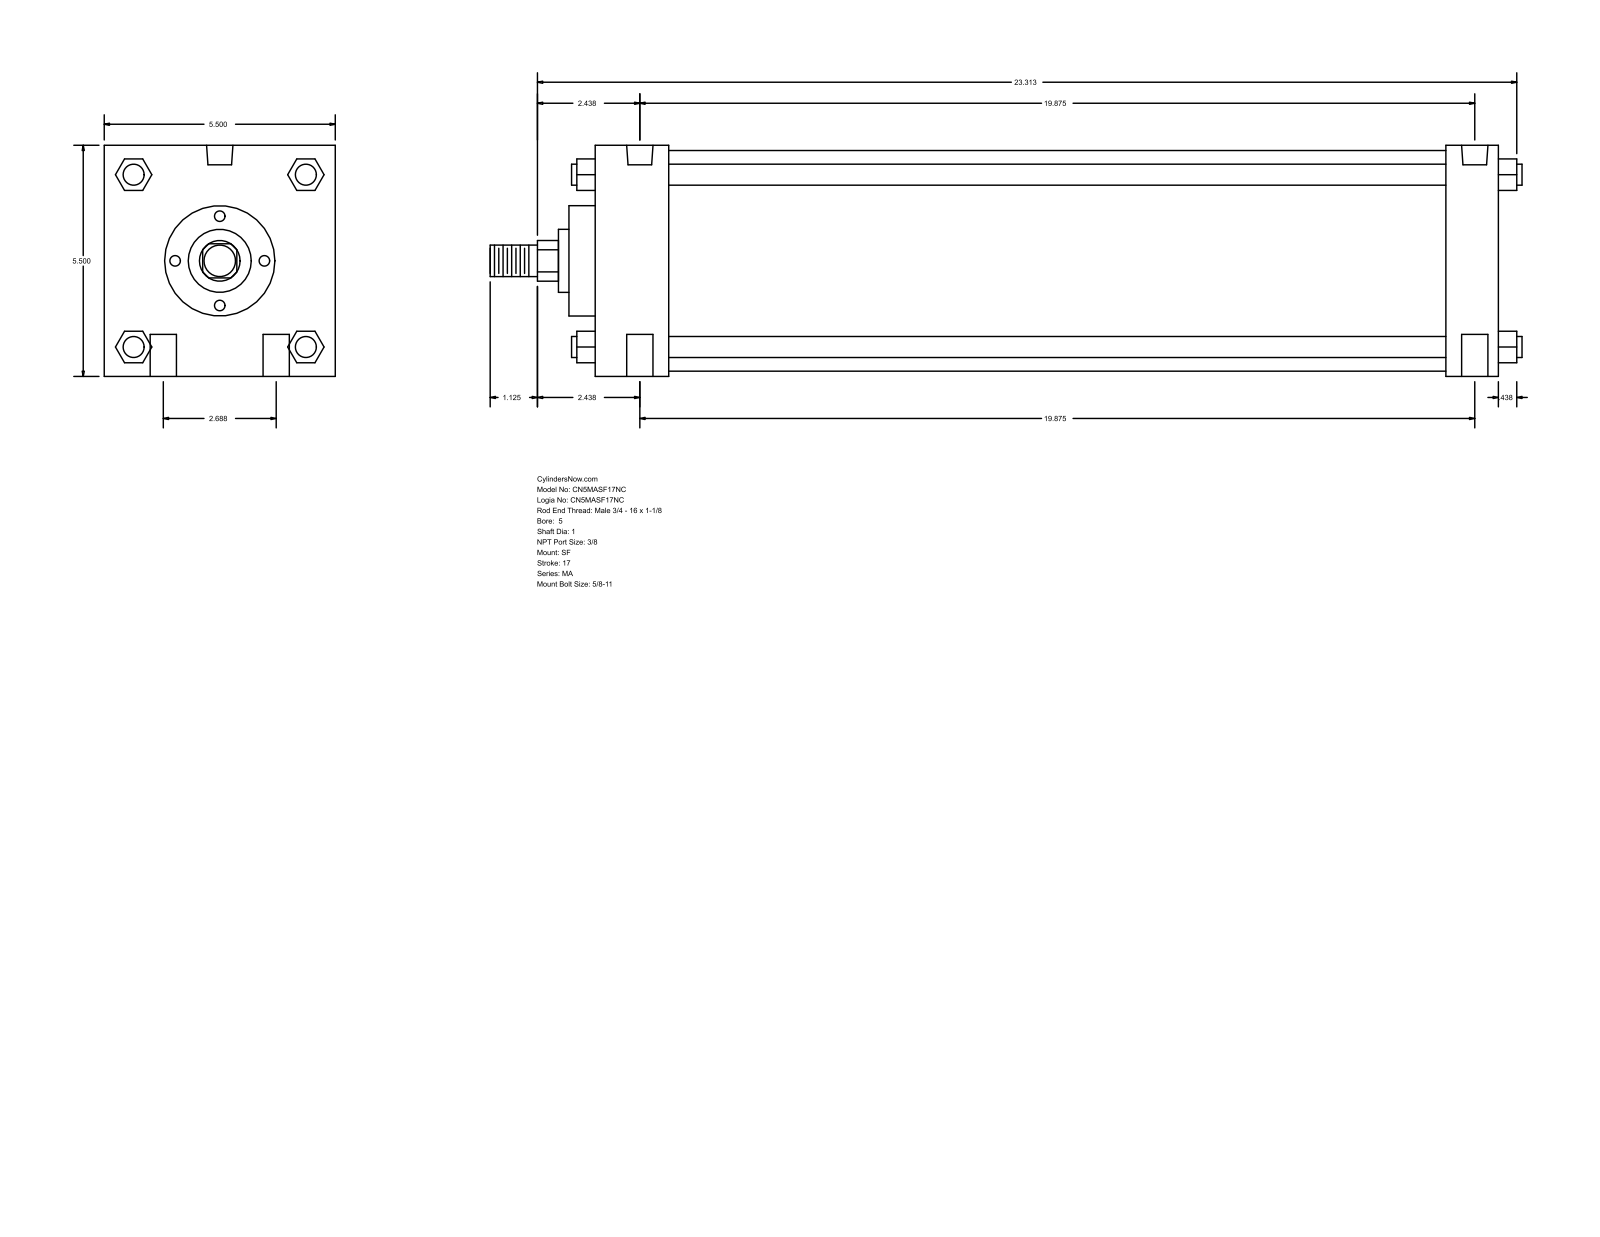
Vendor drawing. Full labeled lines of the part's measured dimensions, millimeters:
Part name (STEP PRODUCT): MA_SF__0500_1
STEP written by: GSSL Pune (CONFIG_CONTROL_DESIGN)
Units: millimetres
Bodies: 0 solids, 126 faces (95 planar, 31 cylindrical, 0 other)
Overall size (bounding box): 623.89 × 139.7 × 139.7
Round holes (diameter × count): ⌀15.88 ×4, ⌀11.11 ×2, ⌀15.93 ×2
Round bosses / shafts (diameter × count): ⌀12.7 ×4, ⌀133.35 ×1, ⌀66.67 ×1, ⌀38.1 ×1, ⌀25.4 ×1, ⌀19.05 ×1
Partial cylindrical surfaces — rounded edges, fillets, slot ends (radius × count): R12.29 ×1
Main face-to-face distances: 139.7, 546.1, 44.46, 514.35, 469.89, 501.64, 31.75, 15.87, 60.33, 530.22
Hole centre spacings: 34.13, 505.98, 504.83, 68.26, 509.42, 495.31
